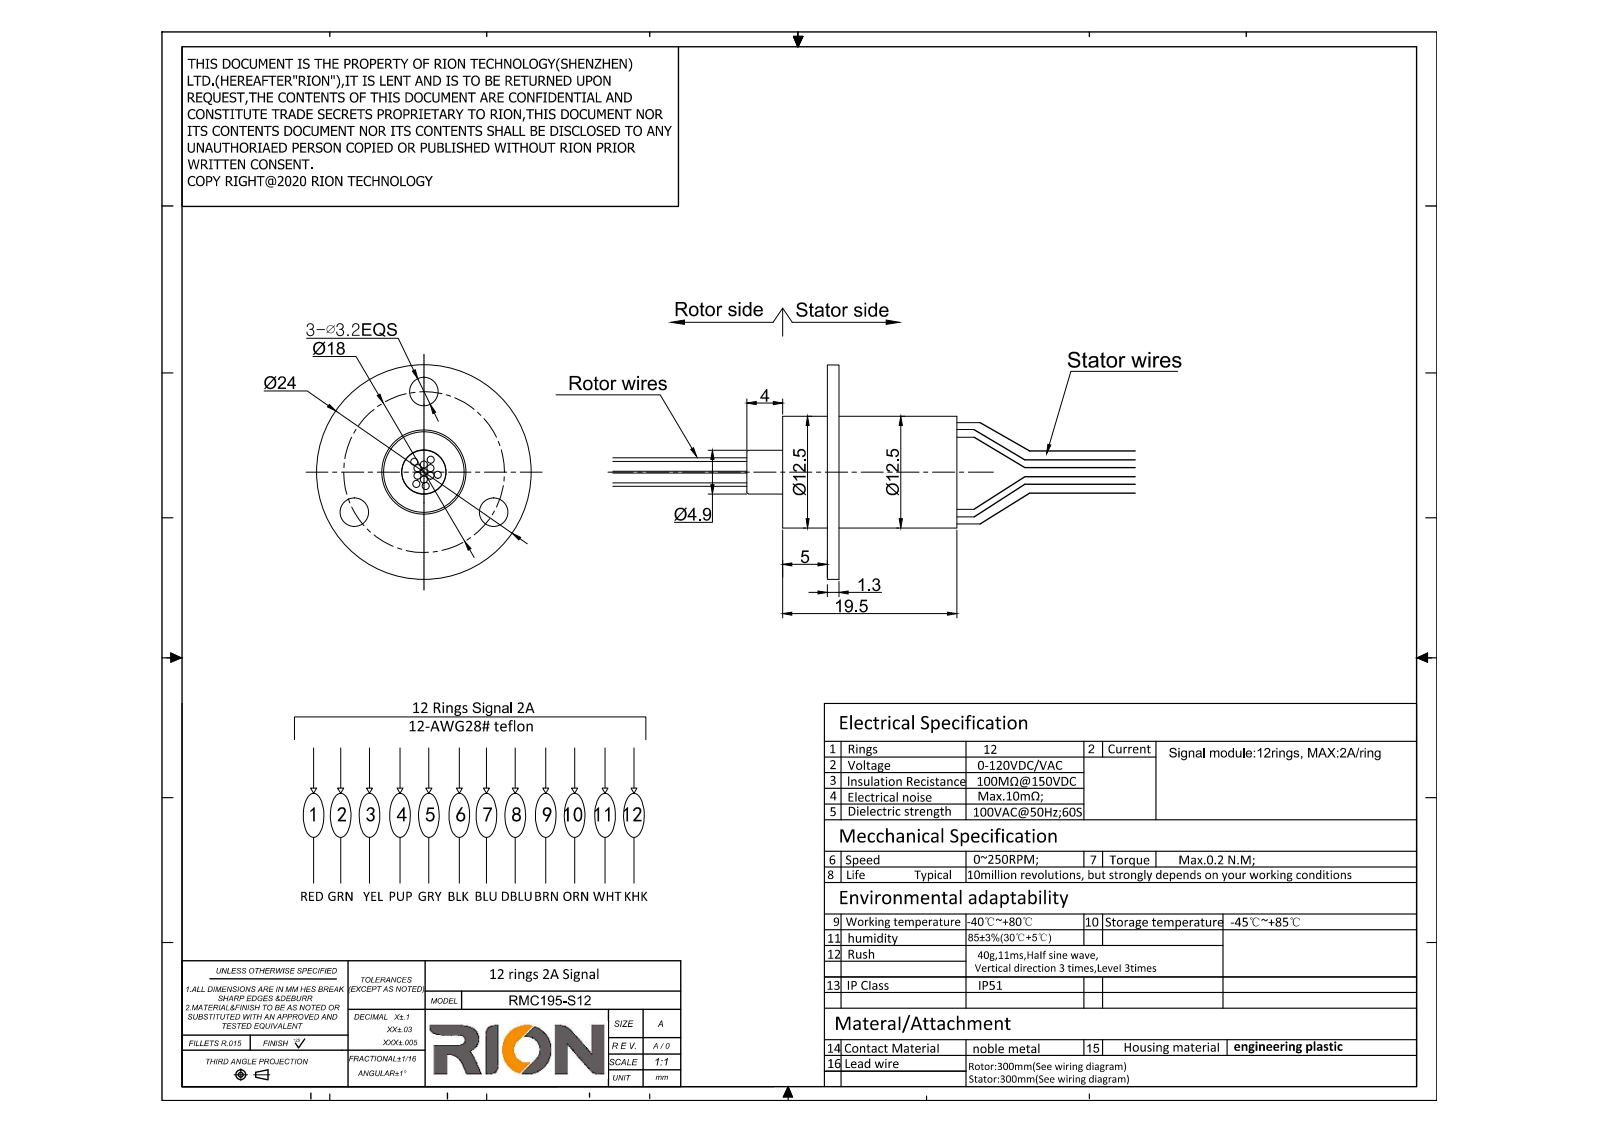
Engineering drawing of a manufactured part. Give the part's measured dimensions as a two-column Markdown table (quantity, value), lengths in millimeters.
| quantity | value |
| --- | --- |
| part name | MMC195 |
| STEP written by | SolidWorks 2014 (CONFIG_CONTROL_DESIGN) |
| units | millimeters |
| bodies | 1 solid, 113 faces (43 planar, 70 cylindrical, 0 other) |
| overall size | 33.3 × 24 × 24 |
| volume | 2 919 mm³ |
| surface area | 2 201 mm² |
| round holes (diameter × count) | 3.2 × 3, 9.4 × 1, 11.2 × 1 |
| round bosses / shafts (diameter × count) | 0.8 × 24, 24 × 1, 12.5 × 1, 11.1 × 1, 9.2 × 1, 4.9 × 1 |
| main face-to-face distances | 1.3, 5, 14.5, 13.2, 6.3, 19.5, 9, 4, 10.3, 23.5 |
| hole center spacings | 9, 15.59, 15.58 |
